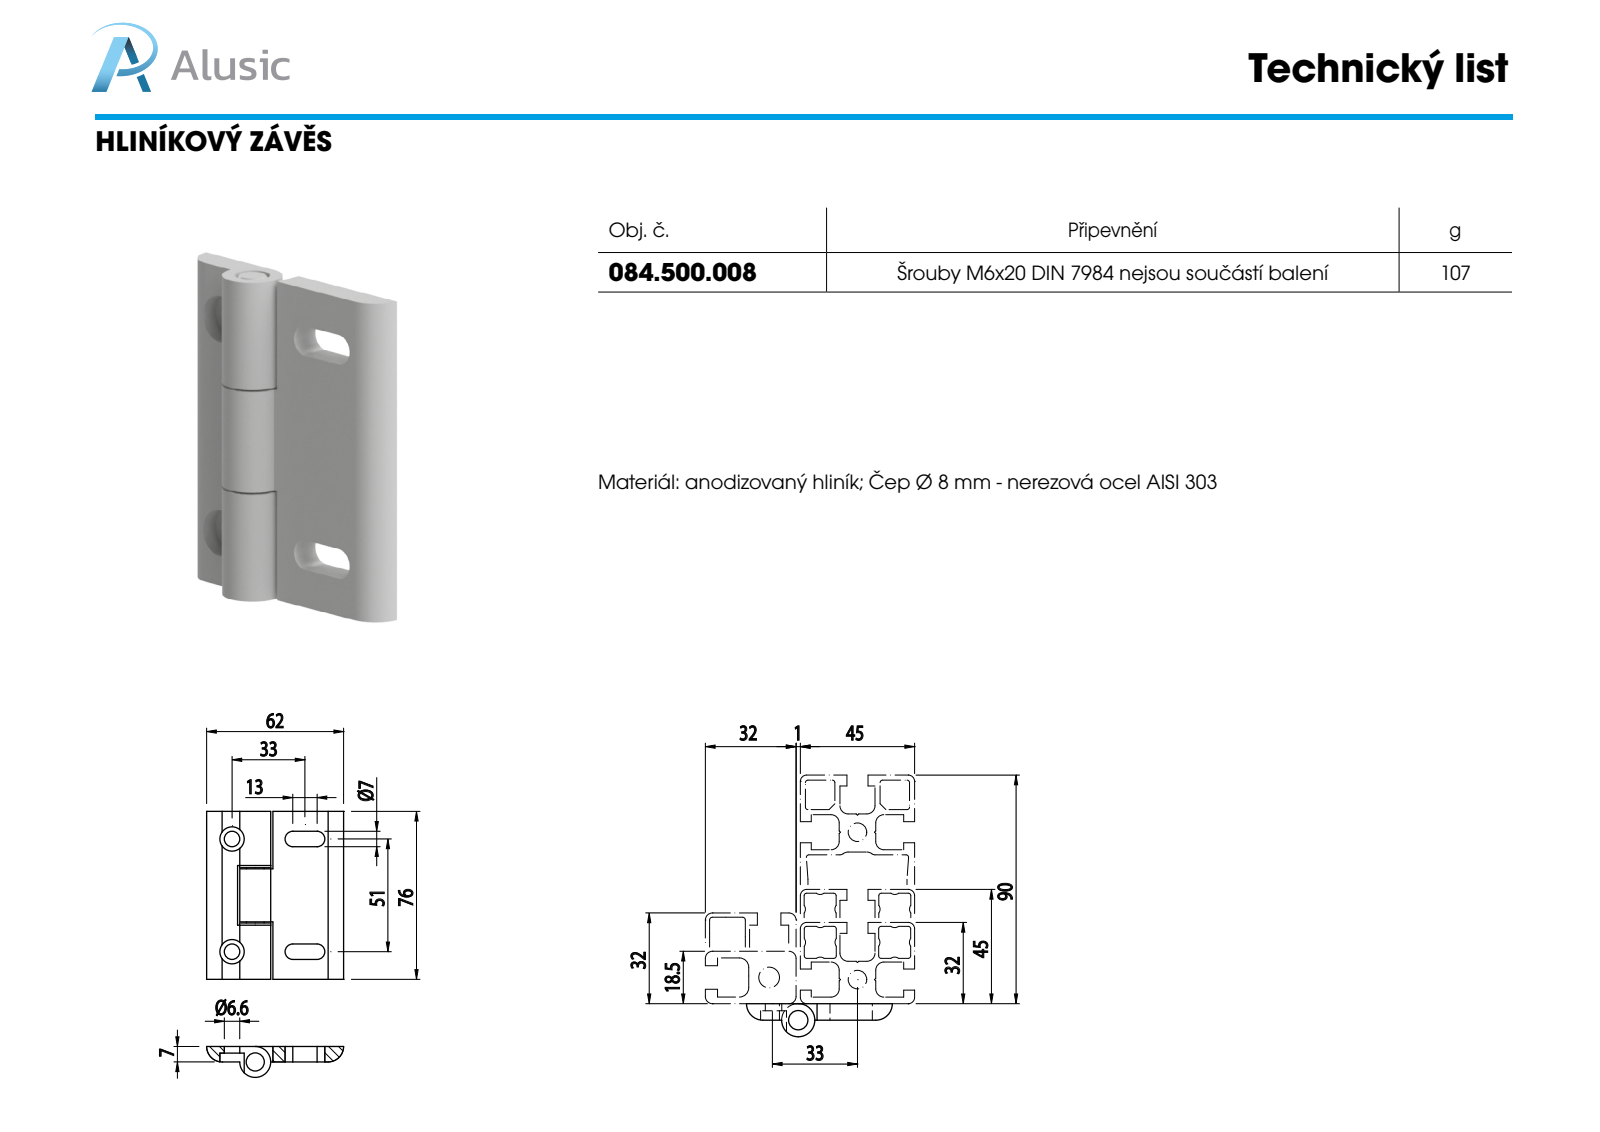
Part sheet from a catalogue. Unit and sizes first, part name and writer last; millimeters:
Units: millimetres
Overall size (bounding box): 76 × 62 × 14.1
Round holes (diameter × count): ⌀7 ×2, ⌀11 ×2, ⌀8.1 ×1, ⌀8.2 ×1
Round bosses / shafts (diameter × count): ⌀14.1 ×1, ⌀14 ×1, ⌀8 ×1
Partial cylindrical surfaces — rounded edges, fillets, slot ends (radius × count): R3.5 ×4, R7 ×2
Main face-to-face distances: 7, 24.5, 76, 51.5, 25.5, 26, 16, 50, 1.5, 27
Hole centre spacings: 51
Volume: 32 853 mm³ · Surface area: 17 422 mm²
Bodies: 5 solids, 190 faces (149 planar, 37 cylindrical, 4 other)
Part name (STEP PRODUCT): 084.500.001.C; 084.500.008a_084.500.001.A; PERNO CERNIERA_084.500.008 A; 084.500.008 (+1 more)
STEP written by: SolidWorks 2018 (AUTOMOTIVE_DESIGN)
